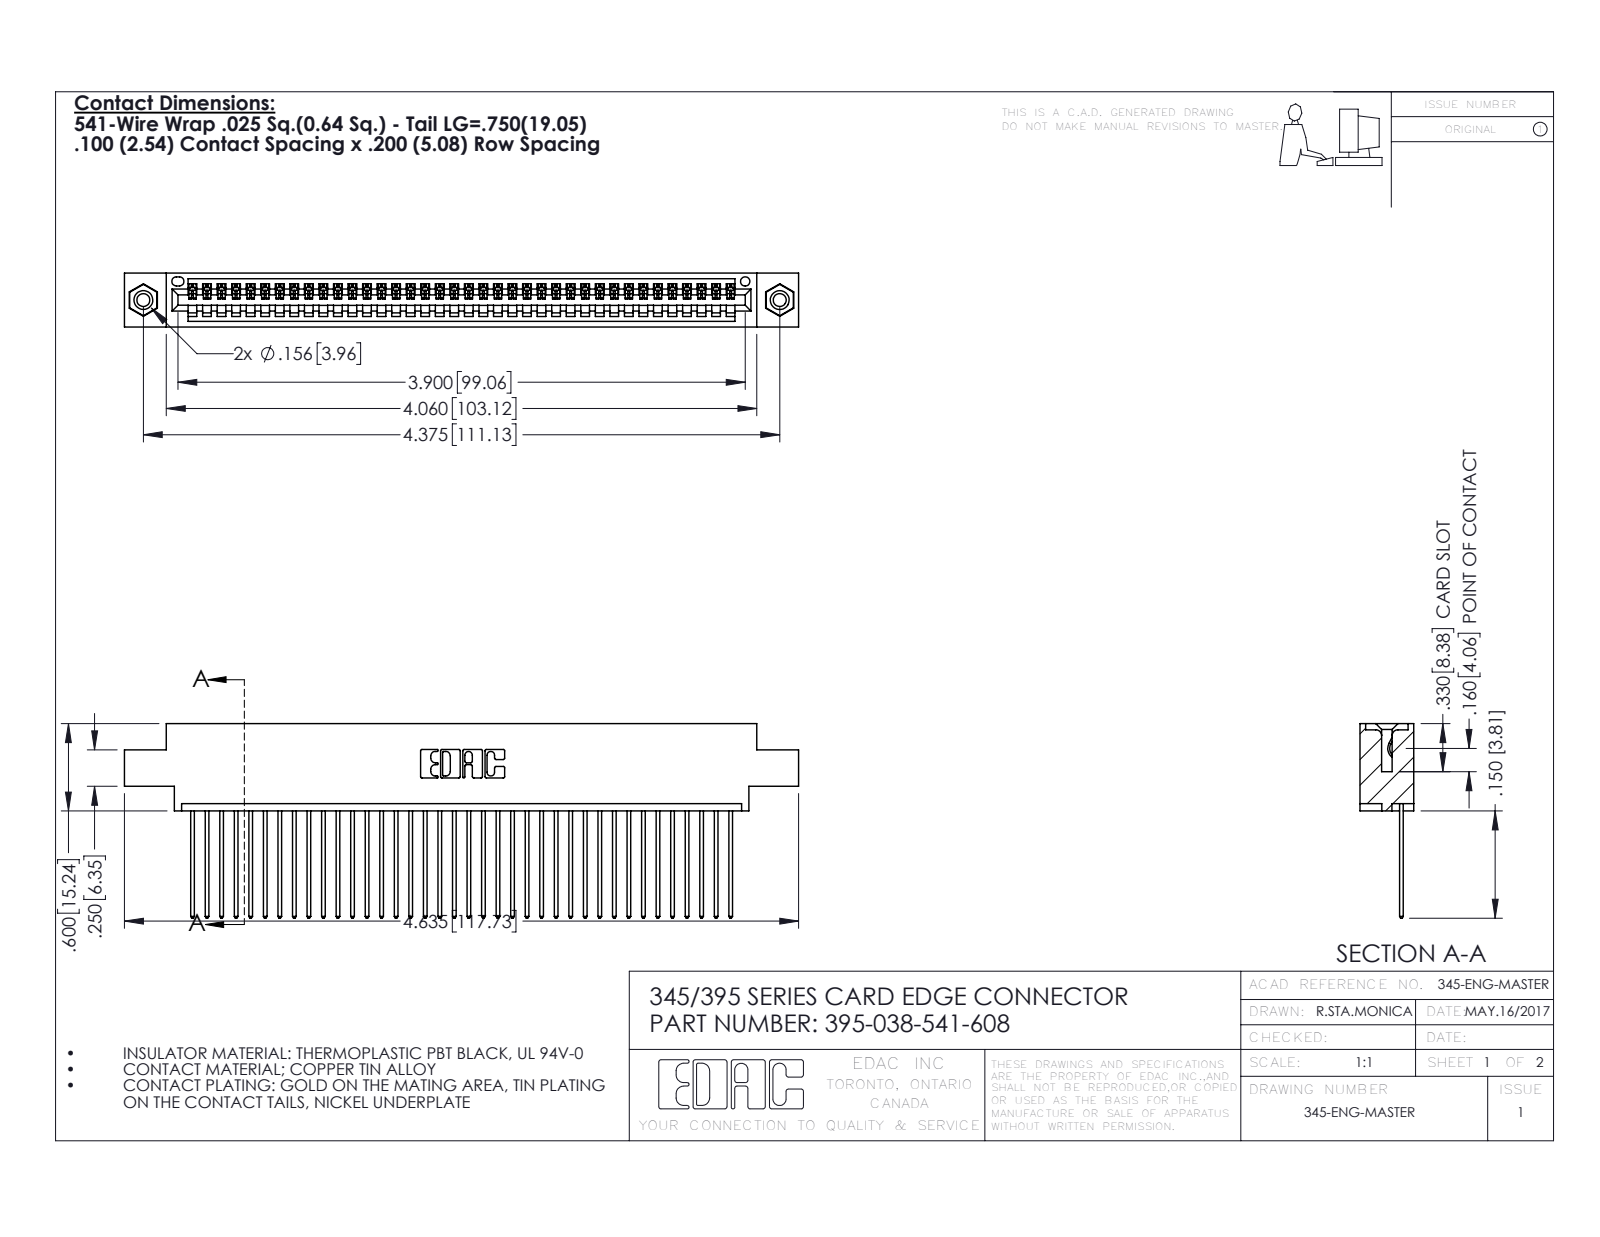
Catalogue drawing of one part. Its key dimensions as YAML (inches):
part_name: "345-292-001_345-293-141; 345-250-001_345-250-003-102; 345 Part_0.170 Offset - 0.156 Dia-TI; 395-038-541-608"
step_written_by: "SolidWorks 2016 (CONFIG_CONTROL_DESIGN)"
units: inches
bodies: {solids: 41, faces: 2394, planar: 1636, cylindrical: 742, other: 16}
overall_size: [4.635, 1.337, 0.37]
volume: 0.681
surface_area: 24.26
round_holes:
  - {diameter: 0.089, count: 2}
  - {diameter: 0.125, count: 2}
  - {diameter: 0.156, count: 2}
  - {diameter: 0.064, count: 1}
round_bosses_or_shafts:
  - {diameter: 0.155, count: 2}
partial_cylinders:
  - {radius: 0.006, count: 76}
  - {radius: 0.01, count: 76}
  - {radius: 0.01, count: 22}
  - {radius: 0.007, count: 6}
  - {radius: 0.031, count: 6}
  - {radius: 0.026, count: 3}
  - {radius: 0.031, count: 2}
  - {radius: 0.04, count: 2}
face_to_face_distances: [0.072, 0.298, 0.37, 0.098, 0.272, 0.025, 0.2, 0.225, 0.175, 0.149]
hole_center_spacings: [0.27, 4.139, 4.375]
